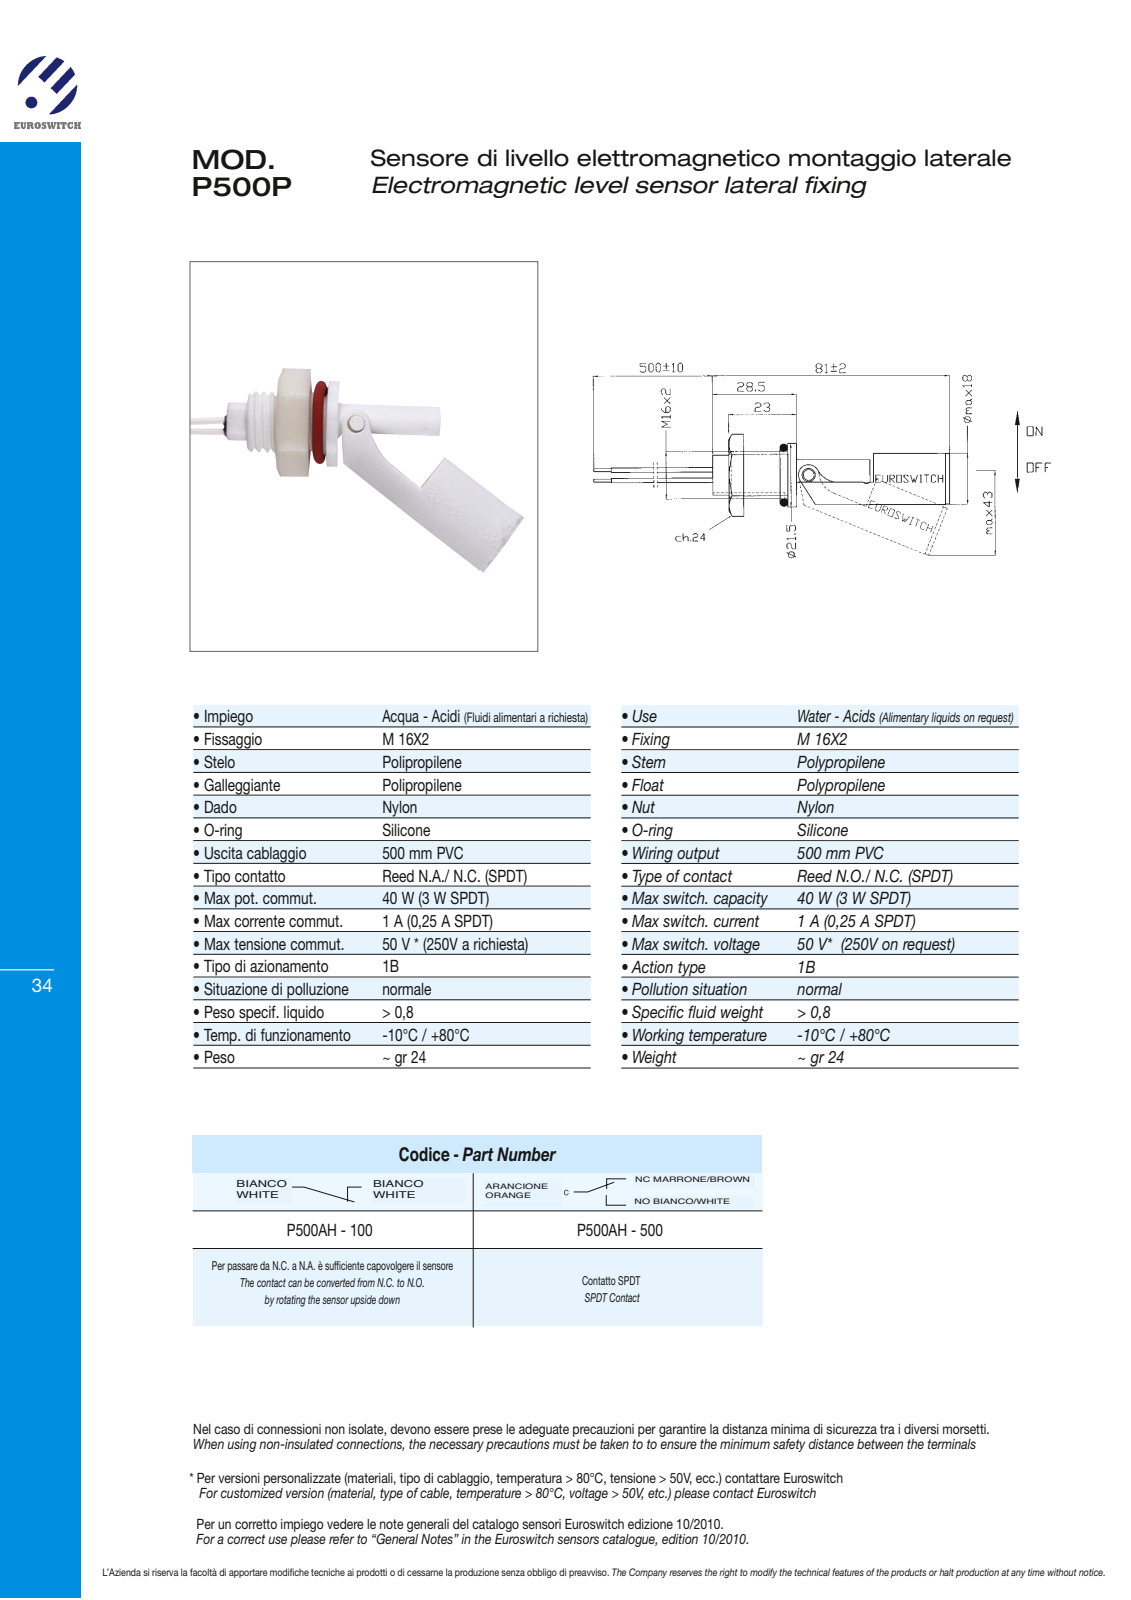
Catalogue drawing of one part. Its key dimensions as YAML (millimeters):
part_name: "P500P"
step_written_by: "SolidWorks 2019 (AUTOMOTIVE_DESIGN)"
units: millimeters
bodies: {solids: 0, faces: 124, planar: 39, cylindrical: 54, other: 31}
overall_size: [559.16, 48.81, 24]
round_holes:
  - {diameter: 4.5, count: 1}
  - {diameter: 8, count: 1}
round_bosses_or_shafts:
  - {diameter: 1.6, count: 2}
  - {diameter: 21.5, count: 1}
  - {diameter: 17.3, count: 1}
  - {diameter: 17, count: 1}
  - {diameter: 16, count: 1}
  - {diameter: 7.5, count: 1}
  - {diameter: 3.7, count: 1}
partial_cylinders:
  - {radius: 3.5, count: 1}
  - {radius: 5.2, count: 1}
  - {radius: 6.75, count: 1}
  - {radius: 7.25, count: 1}
  - {radius: 7.4, count: 1}
  - {radius: 8, count: 1}
  - {radius: 8.65, count: 1}
face_to_face_distances: [6.5, 14.5, 8, 24, 5, 3, 11.5, 25.39, 11, 13]
